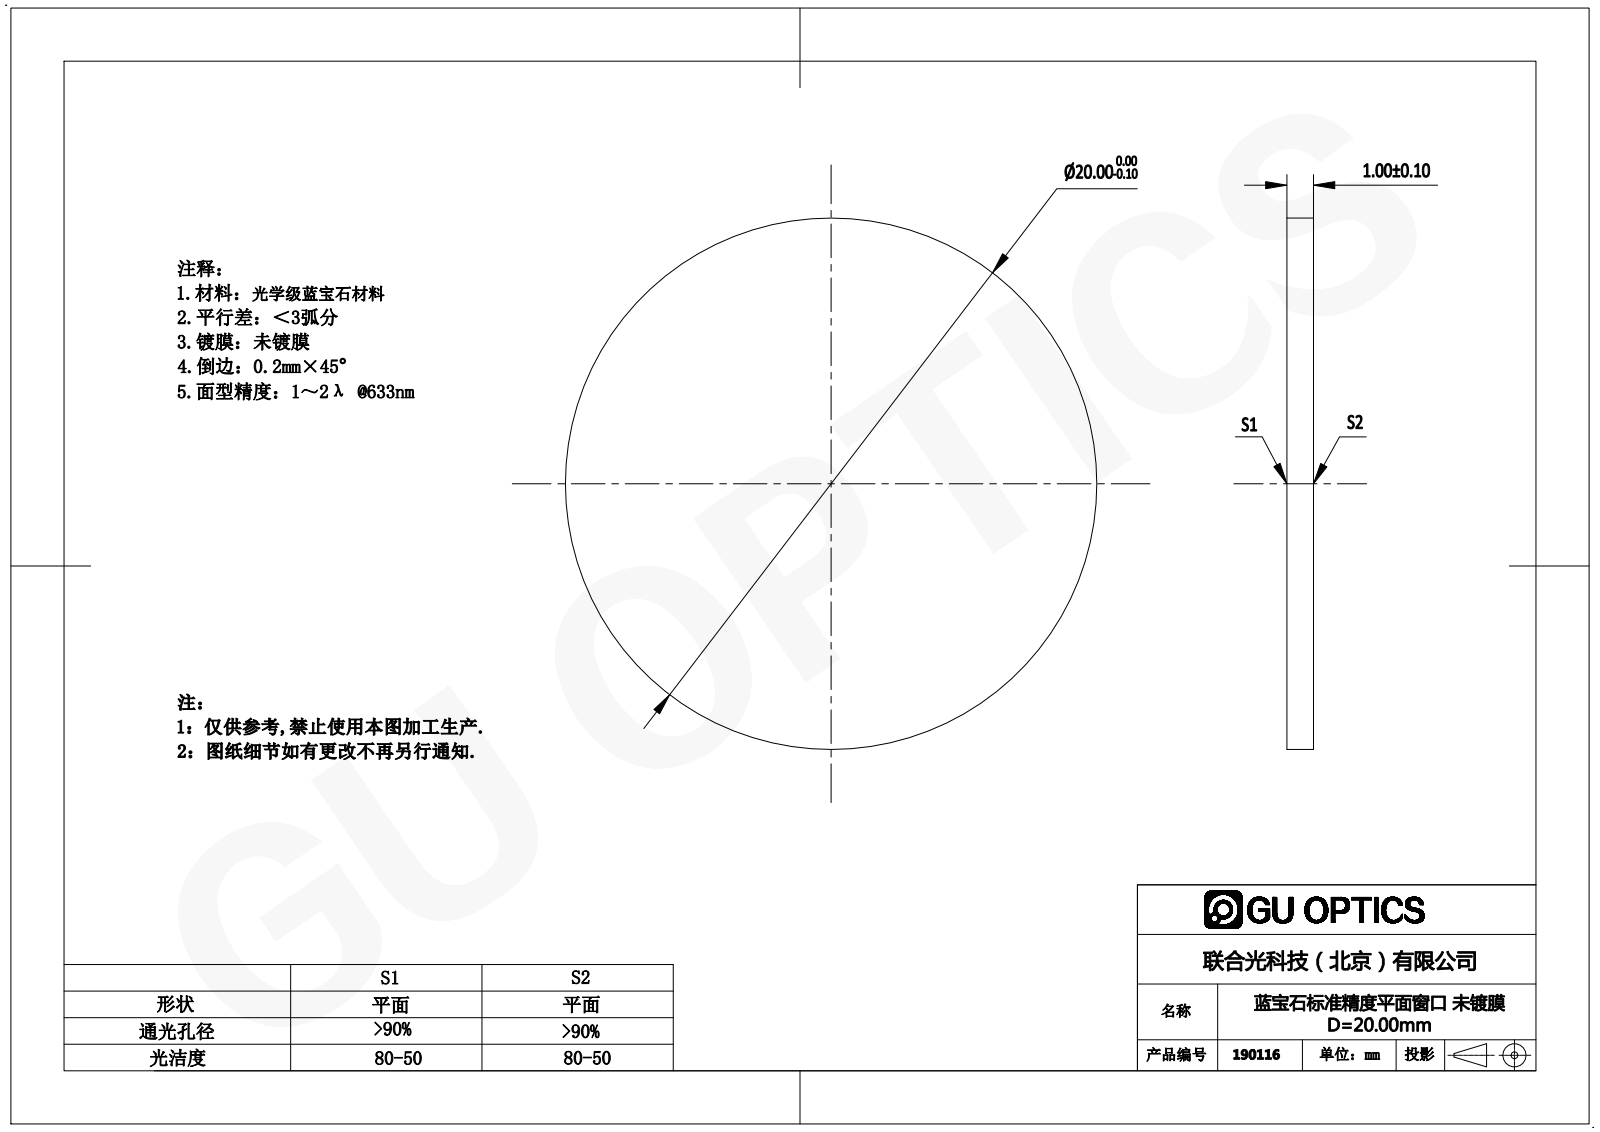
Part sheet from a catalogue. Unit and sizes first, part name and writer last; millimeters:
Units: millimetres
Overall size (bounding box): 20 × 20 × 1
Round bosses / shafts (diameter × count): ⌀20 ×1
Main face-to-face distances: 1
Volume: 314 mm³ · Surface area: 691 mm²
Bodies: 1 solid, 4 faces (2 planar, 2 cylindrical, 0 other)
Part name (STEP PRODUCT): 190116
STEP written by: SolidWorks 2016 (AUTOMOTIVE_DESIGN)
